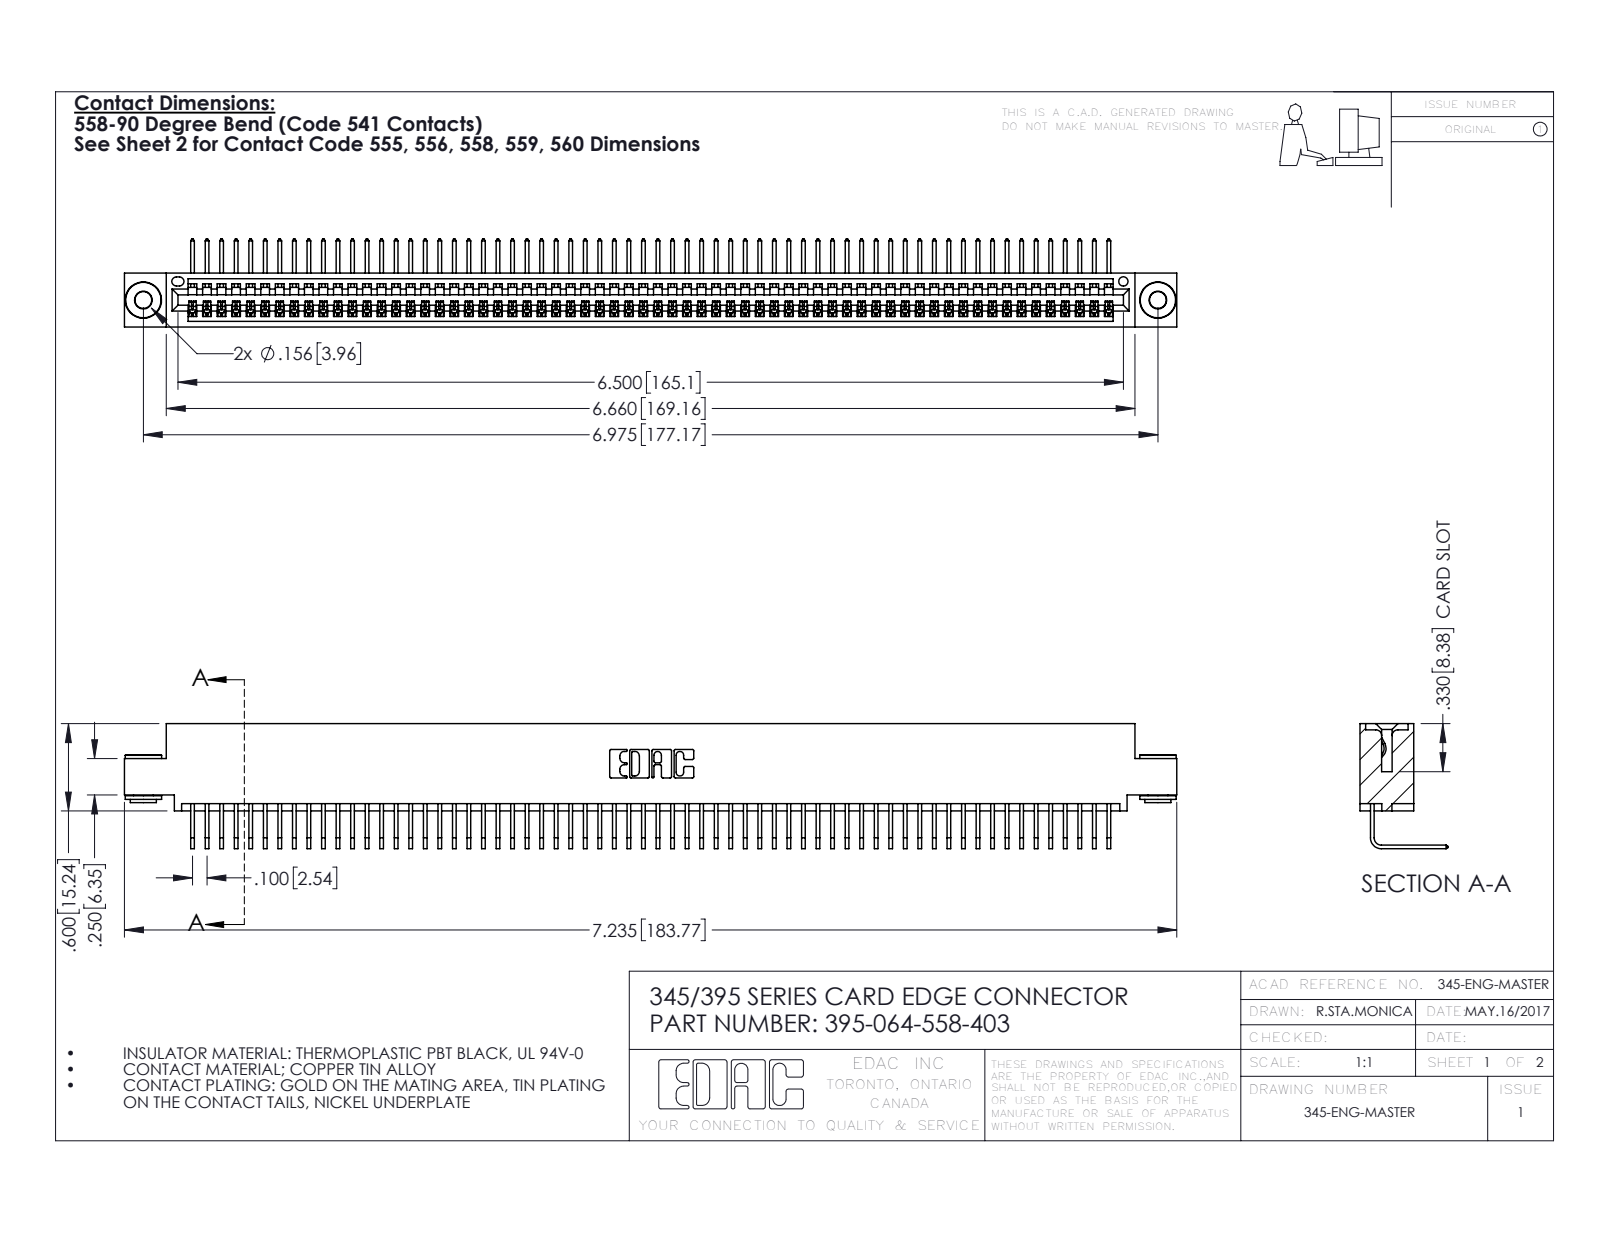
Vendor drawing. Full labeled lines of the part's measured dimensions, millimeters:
Part name (STEP PRODUCT): 395-064-558-403; 345 Part_0.110 Offset - 0.156 Dia-TH; 345-250-002_345-250-002-102; 345-292-001_558 Tail - 2
STEP written by: SolidWorks 2016 (CONFIG_CONTROL_DESIGN)
Units: millimetres
Bodies: 67 solids, 4008 faces (2782 planar, 1218 cylindrical, 8 other)
Overall size (bounding box): 183.8 × 21.8 × 15.4
Volume: 17 800 mm³ · Surface area: 25 500 mm²
Round holes (diameter × count): ⌀2.9 ×2, ⌀4 ×2, ⌀1.6 ×1
Round bosses / shafts (diameter × count): ⌀6.4 ×2, ⌀4.6 ×2, ⌀3.5 ×2
Partial cylindrical surfaces — rounded edges, fillets, slot ends (radius × count): R0.2 ×128, R0.3 ×22, R0.2 ×6, R0.8 ×6, R0.7 ×3, R0.8 ×2, R1 ×2, R0.4 ×1
Main face-to-face distances: 1.8, 7.6, 9.4, 5.1, 0.6, 2.5, 6.9, 5.7, 3.8, 1.8
Hole centre spacings: 6.9, 171.2, 177.2
